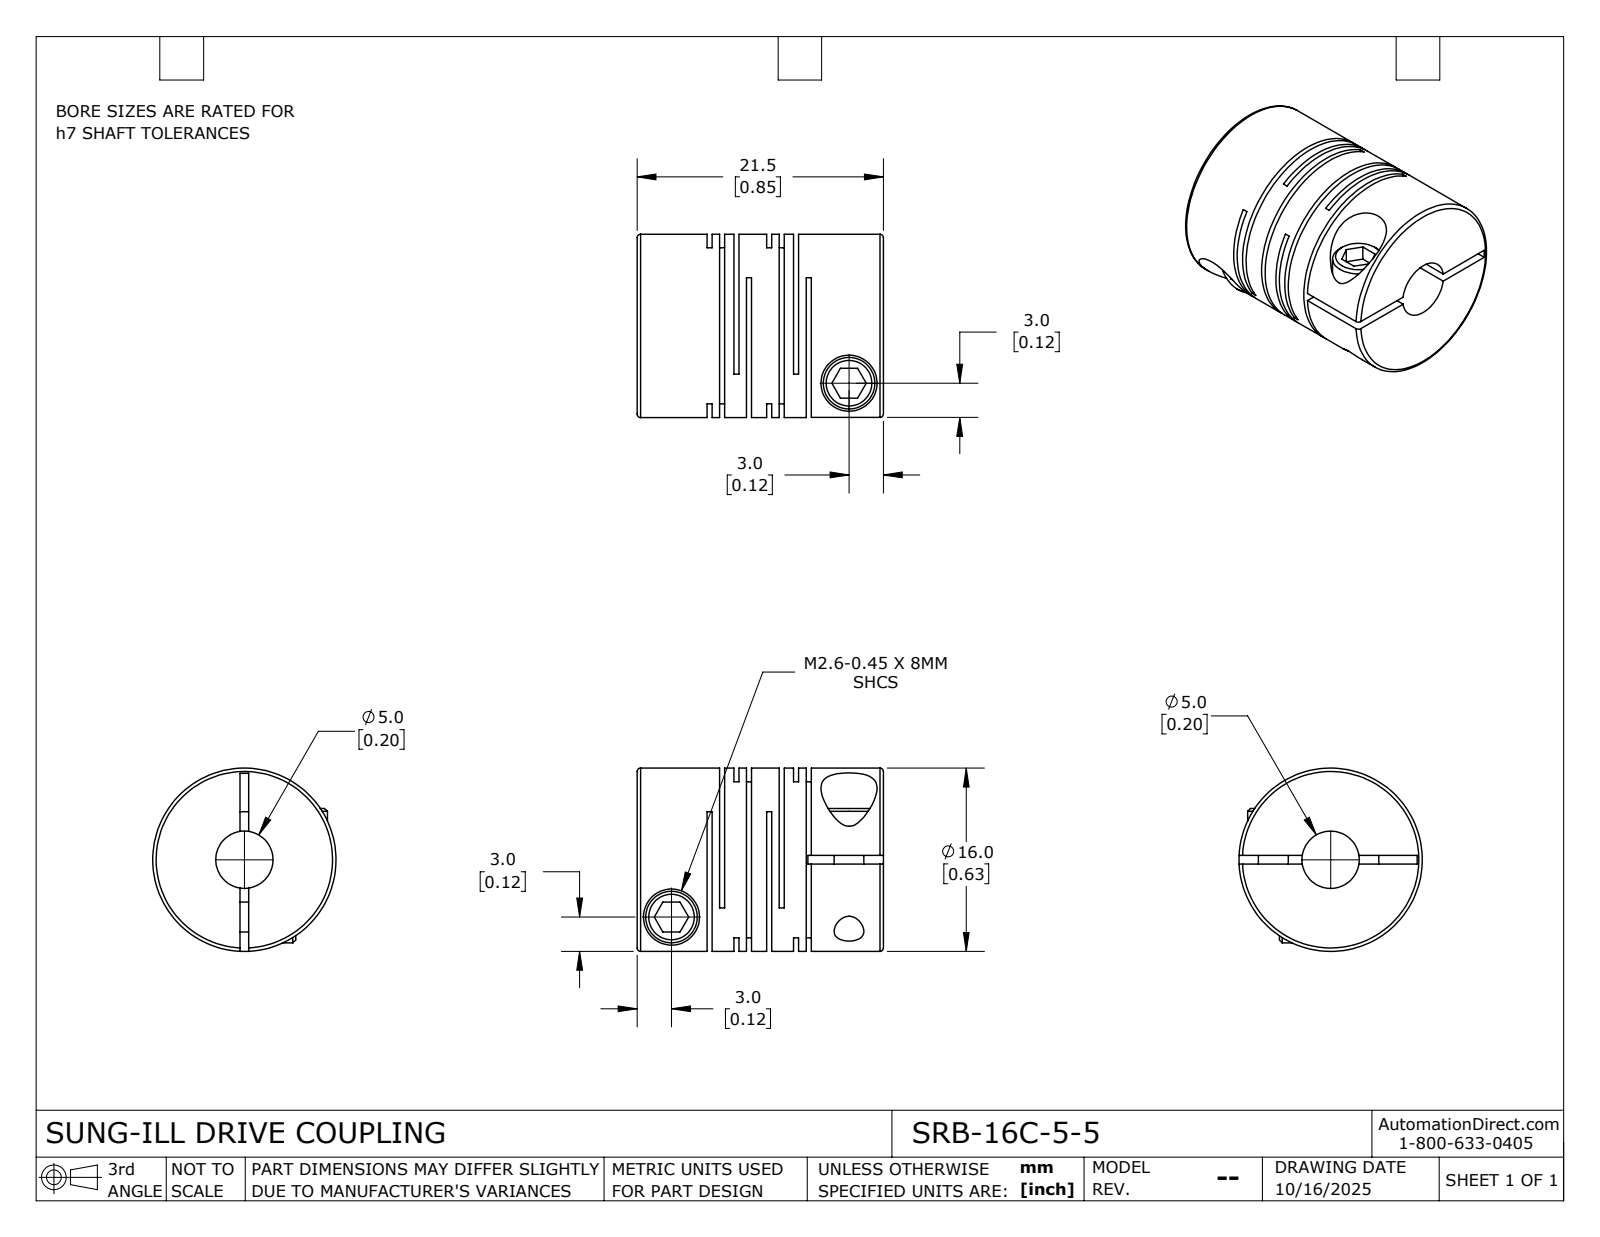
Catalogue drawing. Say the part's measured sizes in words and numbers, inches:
The part is named "SRB-16C-5-5". Its 3-D file was written by "SolidWorks 2024 (CONFIG_CONTROL_DESIGN)". It is 1 solid with 115 faces: 60 planar, 42 cylindrical and 13 other. Overall it measures 0.846 by 0.63 by 0.63 inches. Its volume is 0.195 cubic inches and its surface area 6.764 square inches. Round holes: 2 of diameter 0.102, 2 of diameter 0.193, 1 of diameter 0.197. Round bosses or shafts: 2 of diameter 0.177, 1 of diameter 0.63. The main face-to-face distances are 0.017, 0.205, 0.043, 0.093, 0.026, 0.075, 0.188, 0.049, 0.162, 0.113.
